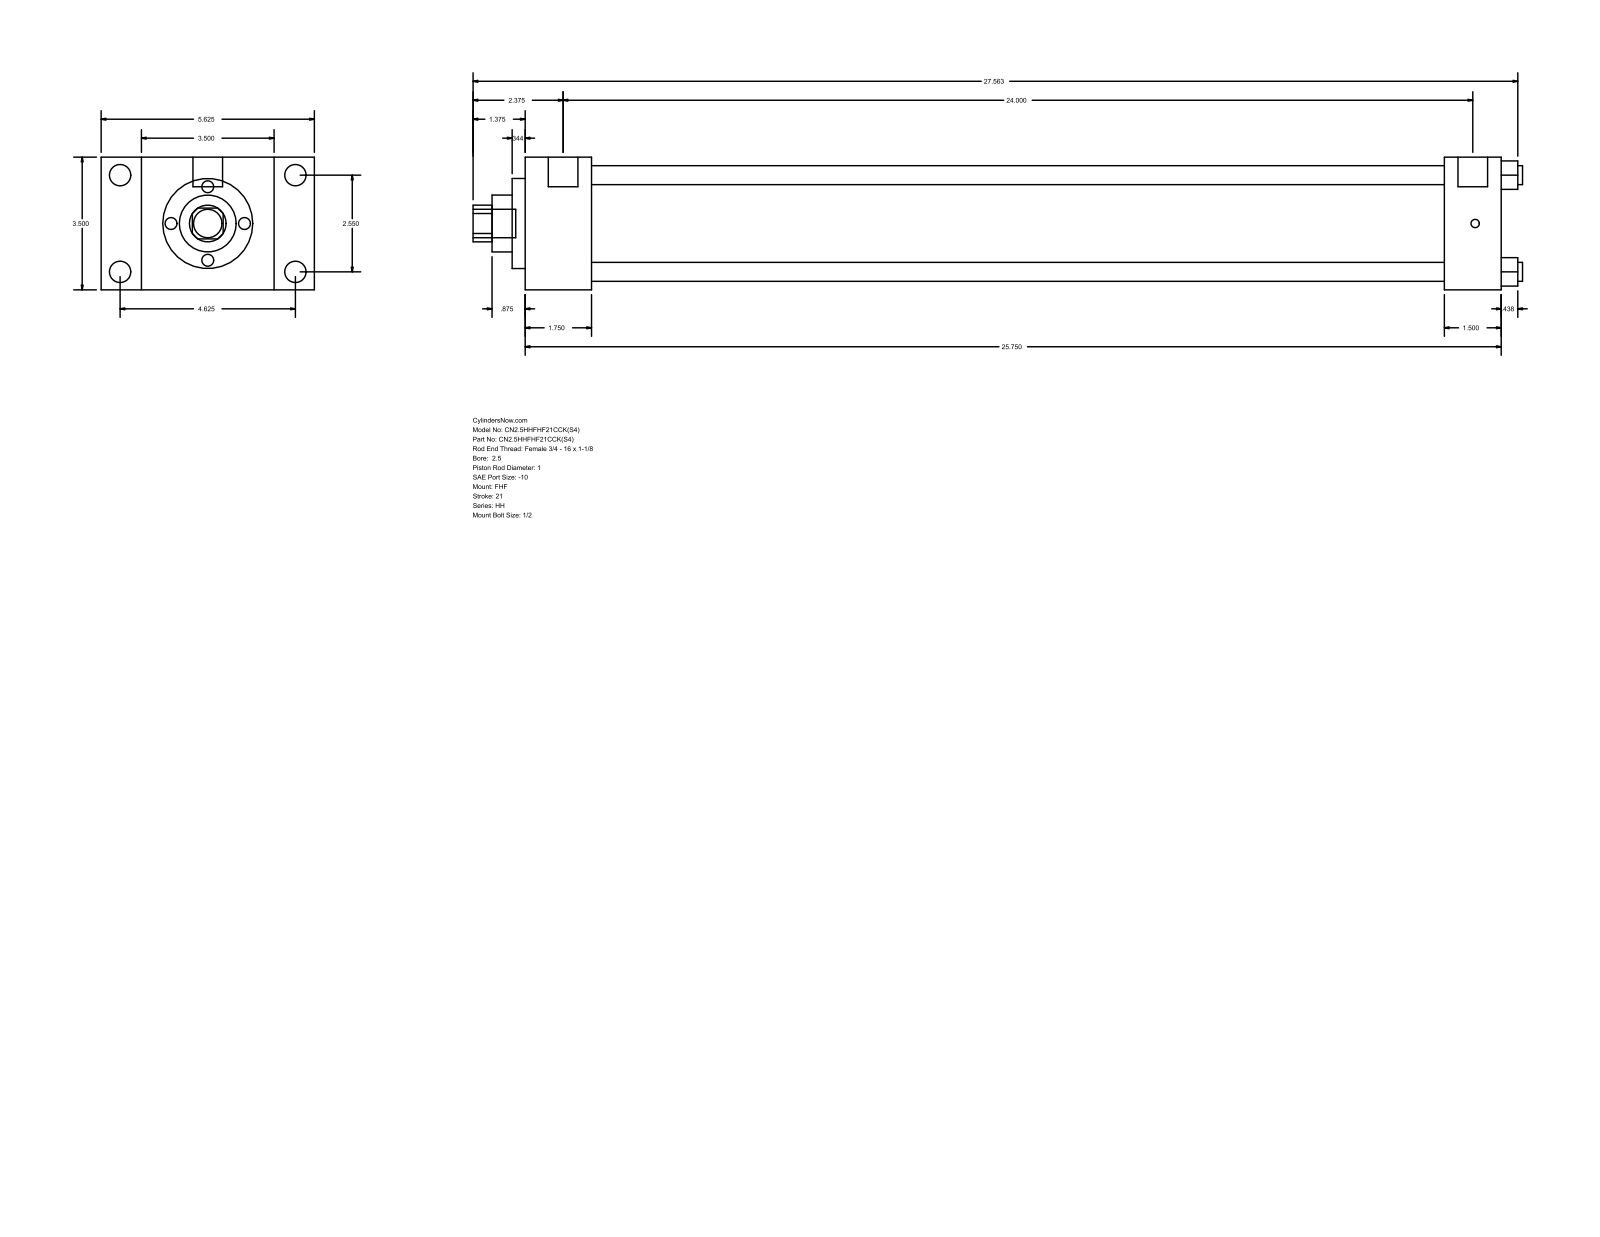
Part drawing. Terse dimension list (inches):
name: HH_FHF__0250_1
written by: GSSL Pune (CONFIG_CONTROL_DESIGN)
unit: in
bodies: 0 solids, 90 faces (61 planar, 29 cylindrical, 0 other)
size: 27.687 × 5.625 × 3.5
holes: 4× ⌀0.5, 1× ⌀1, 1× ⌀1.5, 1× ⌀2.375, 1× ⌀2.875
bosses: 4× ⌀0.563, 4× ⌀0.219, 2× ⌀0.781, 1× ⌀0.75
rounds: 1× R0.484
face distances: 3.5, 1.75, 1.063, 4.563, 25.75, 24, 5.625, 24.25, 22.5, 1.5
hole spacings: 1.803, 2.55, 3.606
